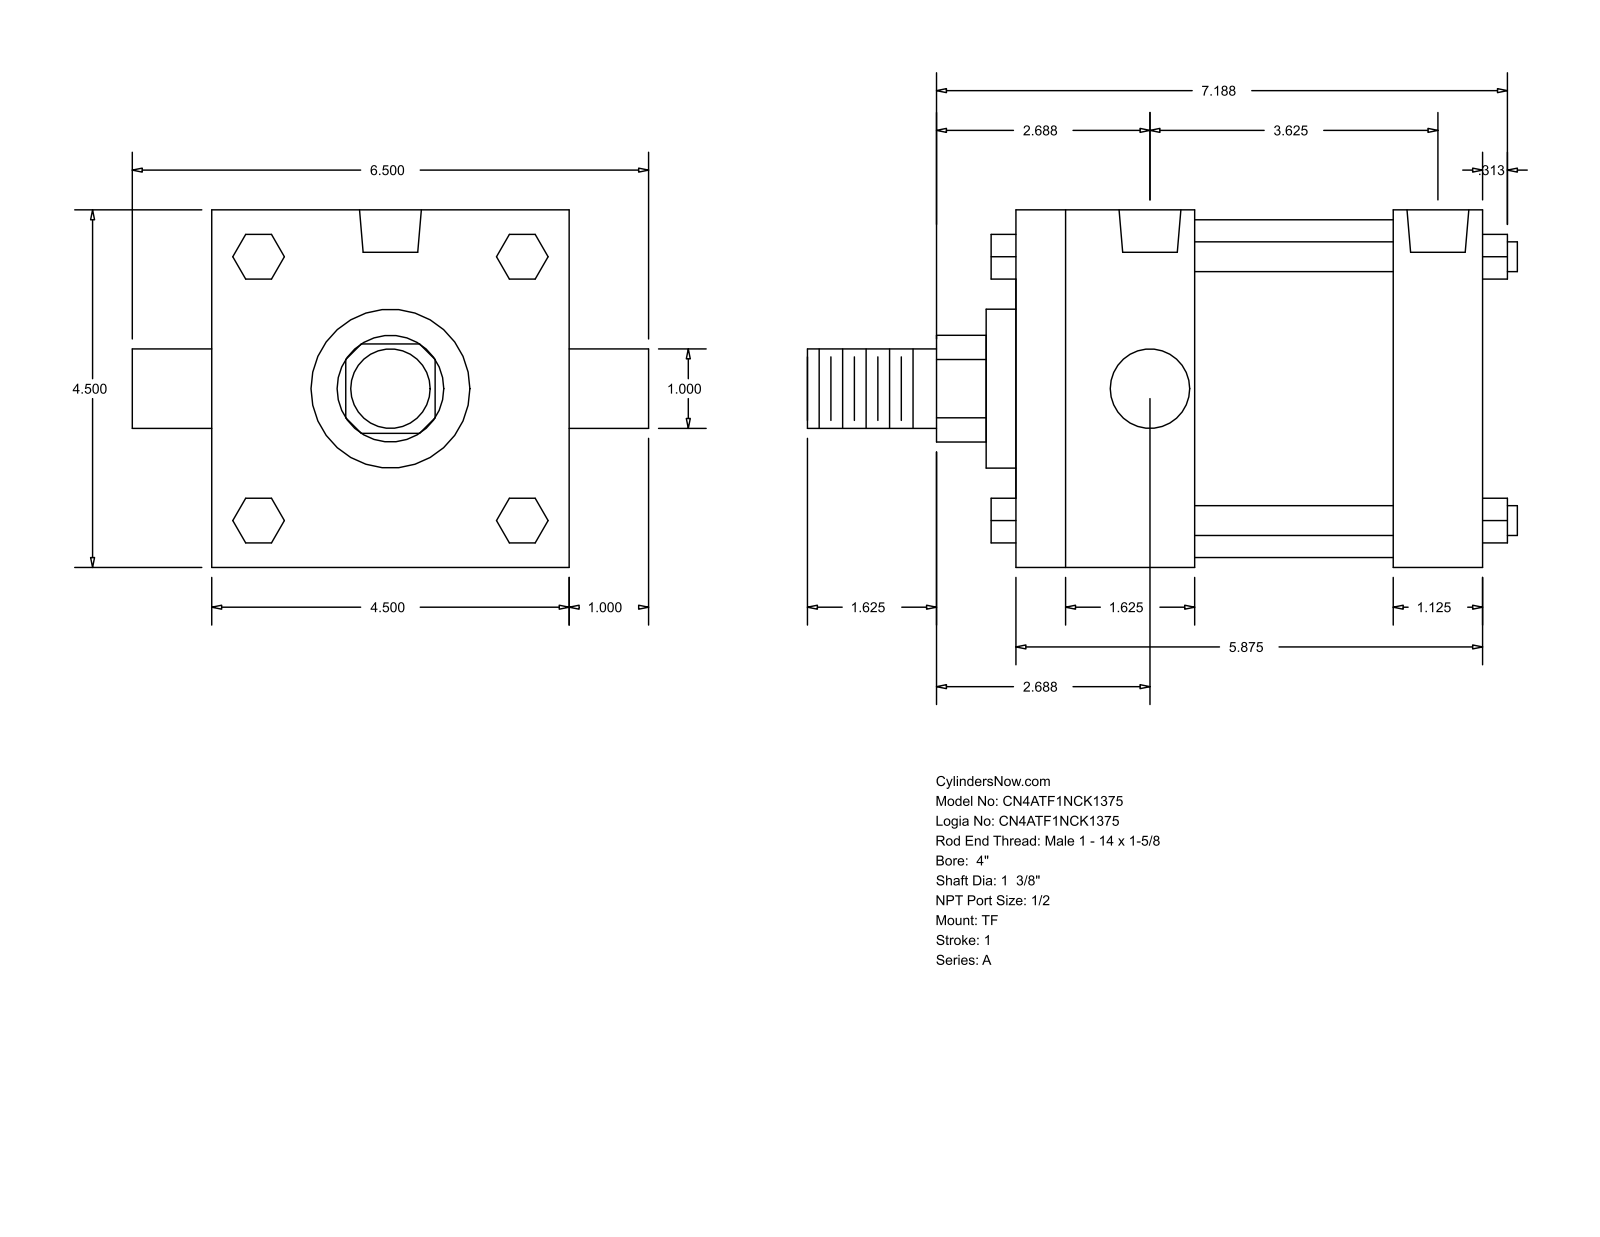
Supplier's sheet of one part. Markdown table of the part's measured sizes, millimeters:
| quantity | value |
| --- | --- |
| part name | A_TF__0400_1.375 |
| STEP written by | GSSL Pune (CONFIG_CONTROL_DESIGN) |
| units | millimeters |
| bodies | 0 solids, 120 faces (92 planar, 28 cylindrical, 0 other) |
| overall size | 227.01 × 165.1 × 114.3 |
| round holes (diameter × count) | 8.73 × 3, 19.77 × 2 |
| round bosses / shafts (diameter × count) | 9.53 × 4, 25.4 × 2, 107.95 × 1, 50.8 × 1, 34.92 × 1 |
| partial cylindrical surfaces (radius × count) | 17.06 × 1 |
| main face-to-face distances | 114.3, 149.22, 57.15, 120.65, 28.57, 63.5, 92.07, 66.67, 14.29, 25.4 |
| hole center spacings | 3.18, 88.9, 85.72, 92.08 |
